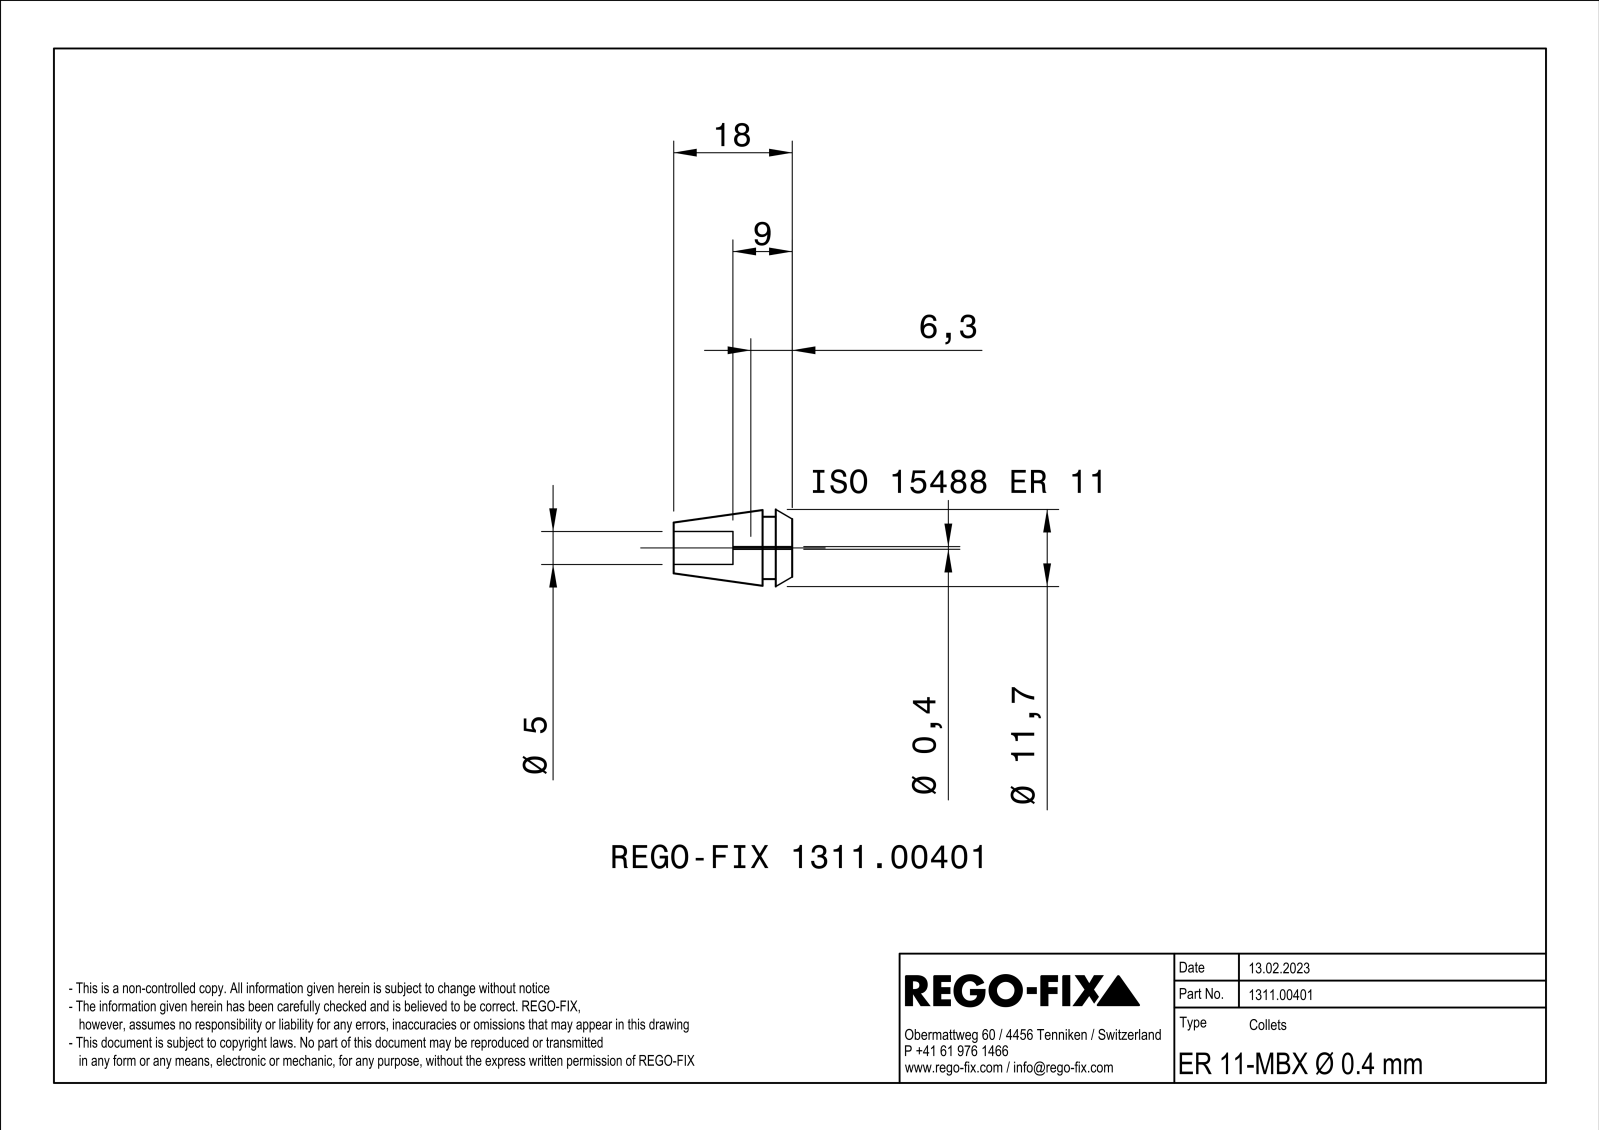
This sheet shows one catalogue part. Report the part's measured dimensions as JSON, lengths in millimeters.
{"part_name": "NOCUT", "step_written_by": "SIEMENS PLM Software Solid Edge ST10 (AUTOMOTIVE_DESIGN)", "units": "millimeters", "bodies": {"solids": 1, "faces": 91, "planar": 26, "cylindrical": 19, "other": 46}, "overall_size": [18, 11.41, 11.39], "volume_mm3": 992, "surface_area_mm2": 1256, "round_holes": [[1.5, 3], [5, 1]], "round_bosses_or_shafts": [[9.5, 1]], "partial_cylinders_radius": [[25, 3], [0.2, 1]], "face_to_face_distances": [0.8, 0.51, 4.5, 9, 18, 13.5, 2.5, 2, 15.5, 6.5], "hole_center_spacings": [1.7, 2.94]}
